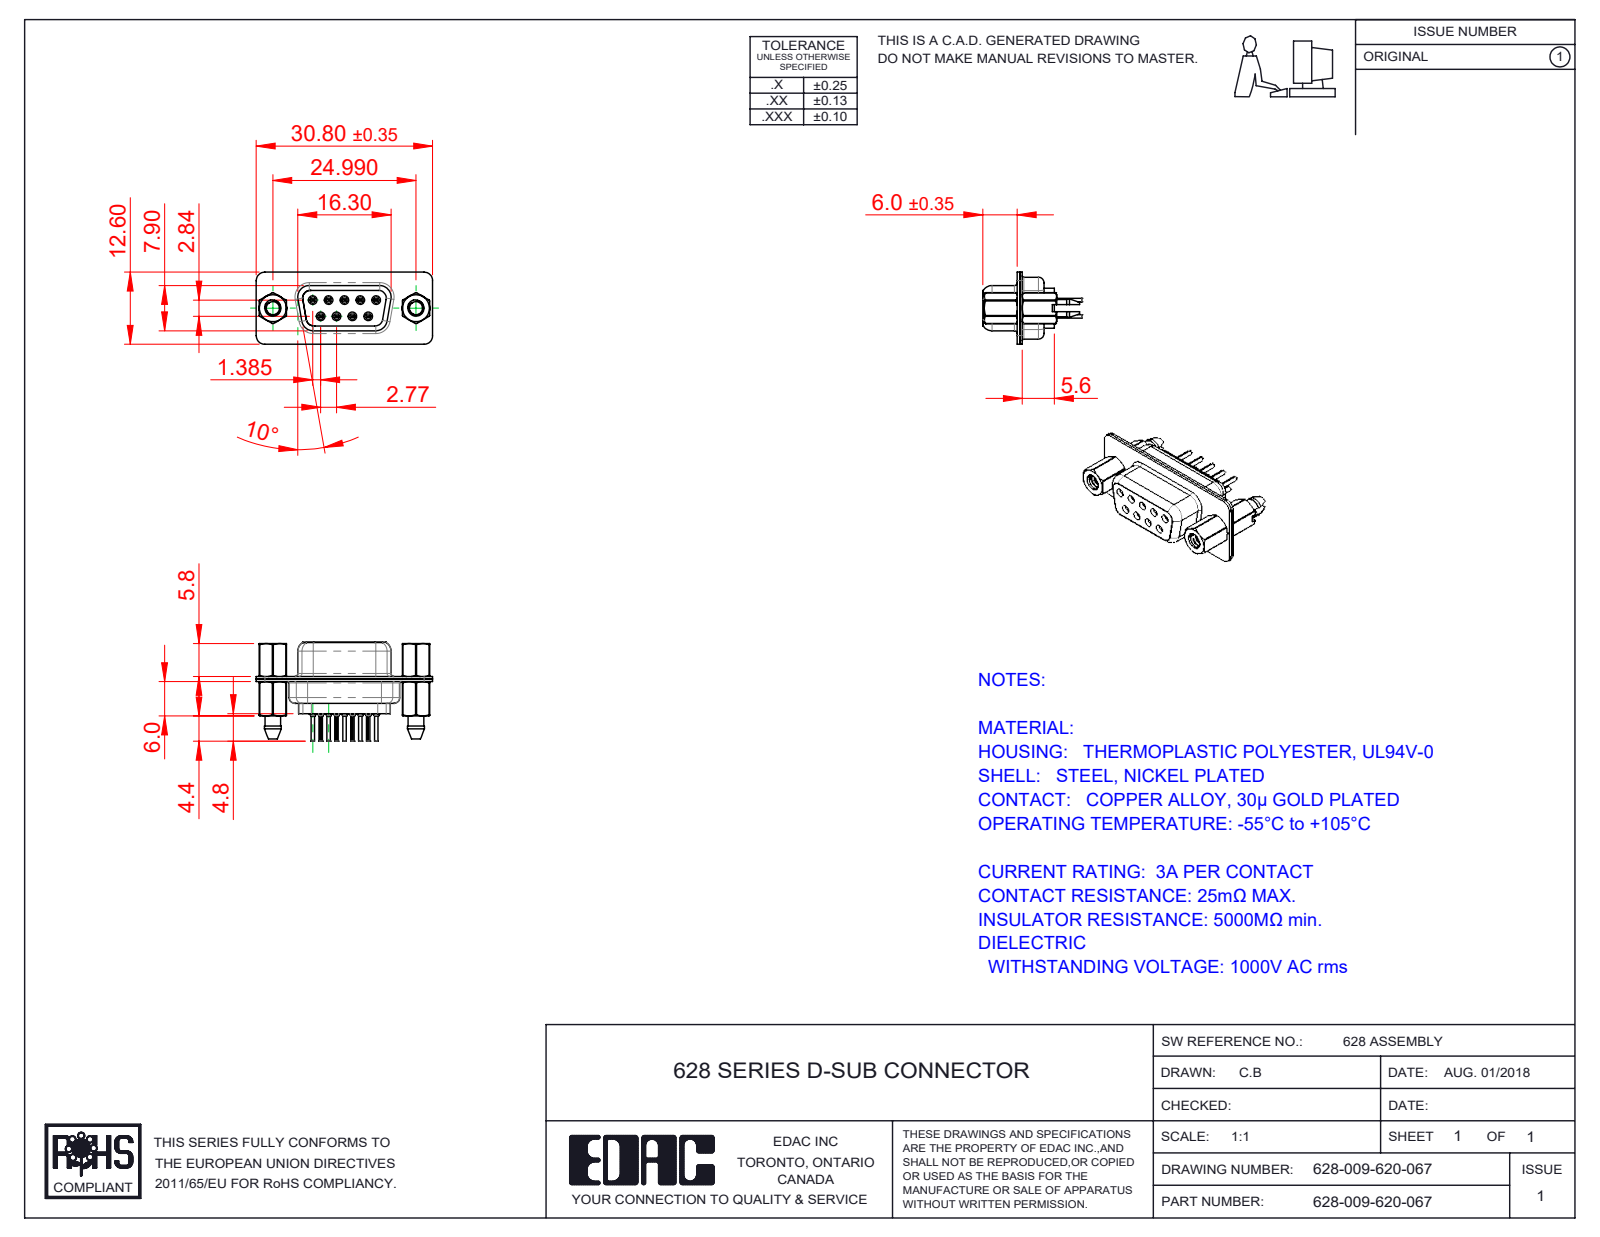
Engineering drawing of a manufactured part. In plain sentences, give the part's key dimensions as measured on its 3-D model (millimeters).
The part is named "628-009-620-067; 628 4-40 Hex Standoff; 628 4-40 Threaded Boardlock_LP; 628 Housing_09 LP (+4 more)". Its 3-D file was written by "SolidWorks 2020 (CONFIG_CONTROL_DESIGN)". It is 16 solids with 1622 faces: 400 planar, 538 cylindrical and 684 other. Overall it measures 30.8 by 17.3 by 12.6 millimeters. Its volume is 2 085 cubic millimeters and its surface area 5 282 square millimeters. Round holes: 9 of diameter 0.2, 9 of diameter 0.8, 9 of diameter 0.9, 9 of diameter 1.1, 9 of diameter 1.6, 5 of diameter 1.7, 2 of diameter 2.26, 2 of diameter 2.29, 2 of diameter 4, 2 of diameter 4.05, 2 of diameter 4.85. Round bosses or shafts: 9 of diameter 2, 9 of diameter 1.5, 9 of diameter 1.2, 9 of diameter 0.6, 2 of diameter 4.95, 2 of diameter 4.8, 2 of diameter 2.79. Partial cylindrical surfaces (rounded edges, fillets, slot ends): 19 of radius 1.5, 18 of radius 0.1, 12 of radius 2, 9 of radius 0.28, 6 of radius 1.35, 6 of radius 1.6, 4 of radius 0.25, 4 of radius 0.5. The main face-to-face distances are 0.45, 0.4, 0.9, 1.9, 8.5, 6.6, 1.4, 12.5, 4.76, 0.5. The hole center spacings are 3.16, 2.77, 5.54, 5.03, 5.04, 8.31, 7.48, 7.49.
